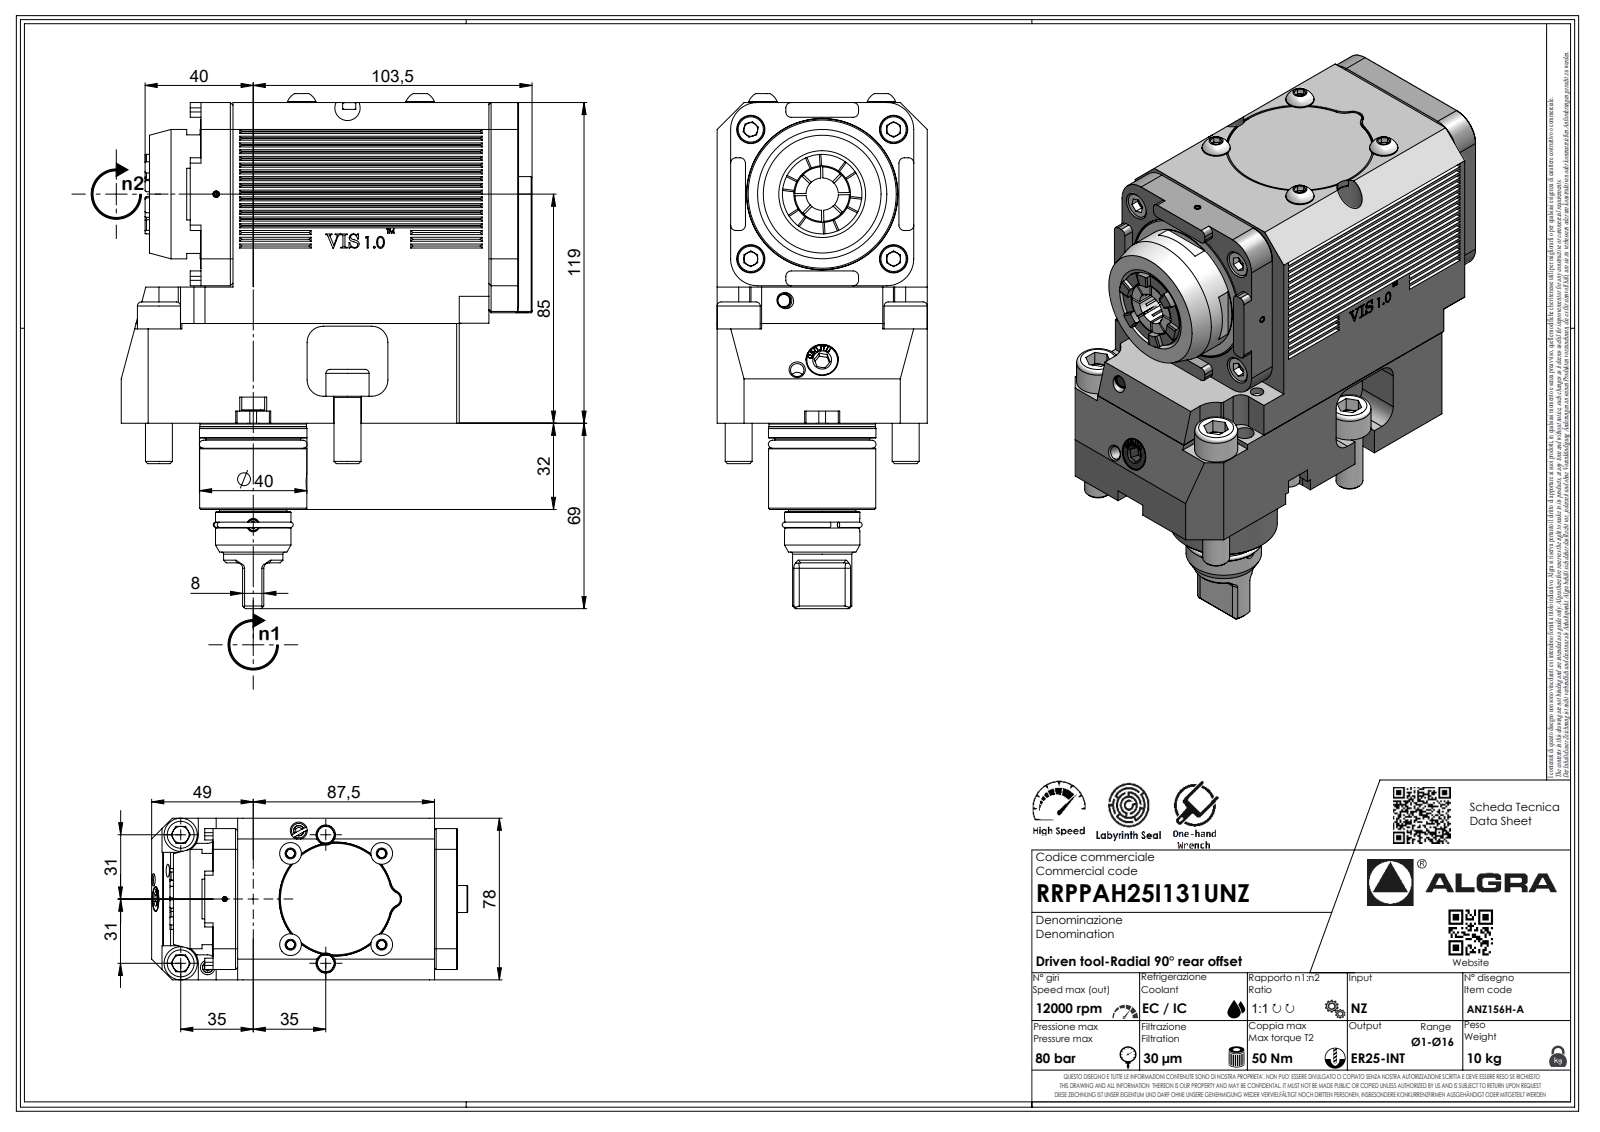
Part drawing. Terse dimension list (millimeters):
name: RRPPAH25I131UNZ
written by: SolidWorks 2023 (AUTOMOTIVE_DESIGN)
unit: mm
bodies: 1 solid, 526 faces (336 planar, 85 cylindrical, 105 other)
size: 187.8 × 152.5 × 78
volume: 1 183 000 mm³; area: 83 375 mm²
holes: 1× ⌀2.1
bosses: 4× ⌀10, 2× ⌀16, 1× ⌀48, 1× ⌀39.9, 1× ⌀39.8, 1× ⌀39.5, 1× ⌀35.1, 1× ⌀28
rounds: 22× R2, 7× R0.33, 7× R0.52, 7× R3.7, 6× R10, 2× R1, 2× R4.1, 2× R8.5
face distances: 78, 119, 11, 22, 5, 50.5, 73, 68.5, 68, 95.9
